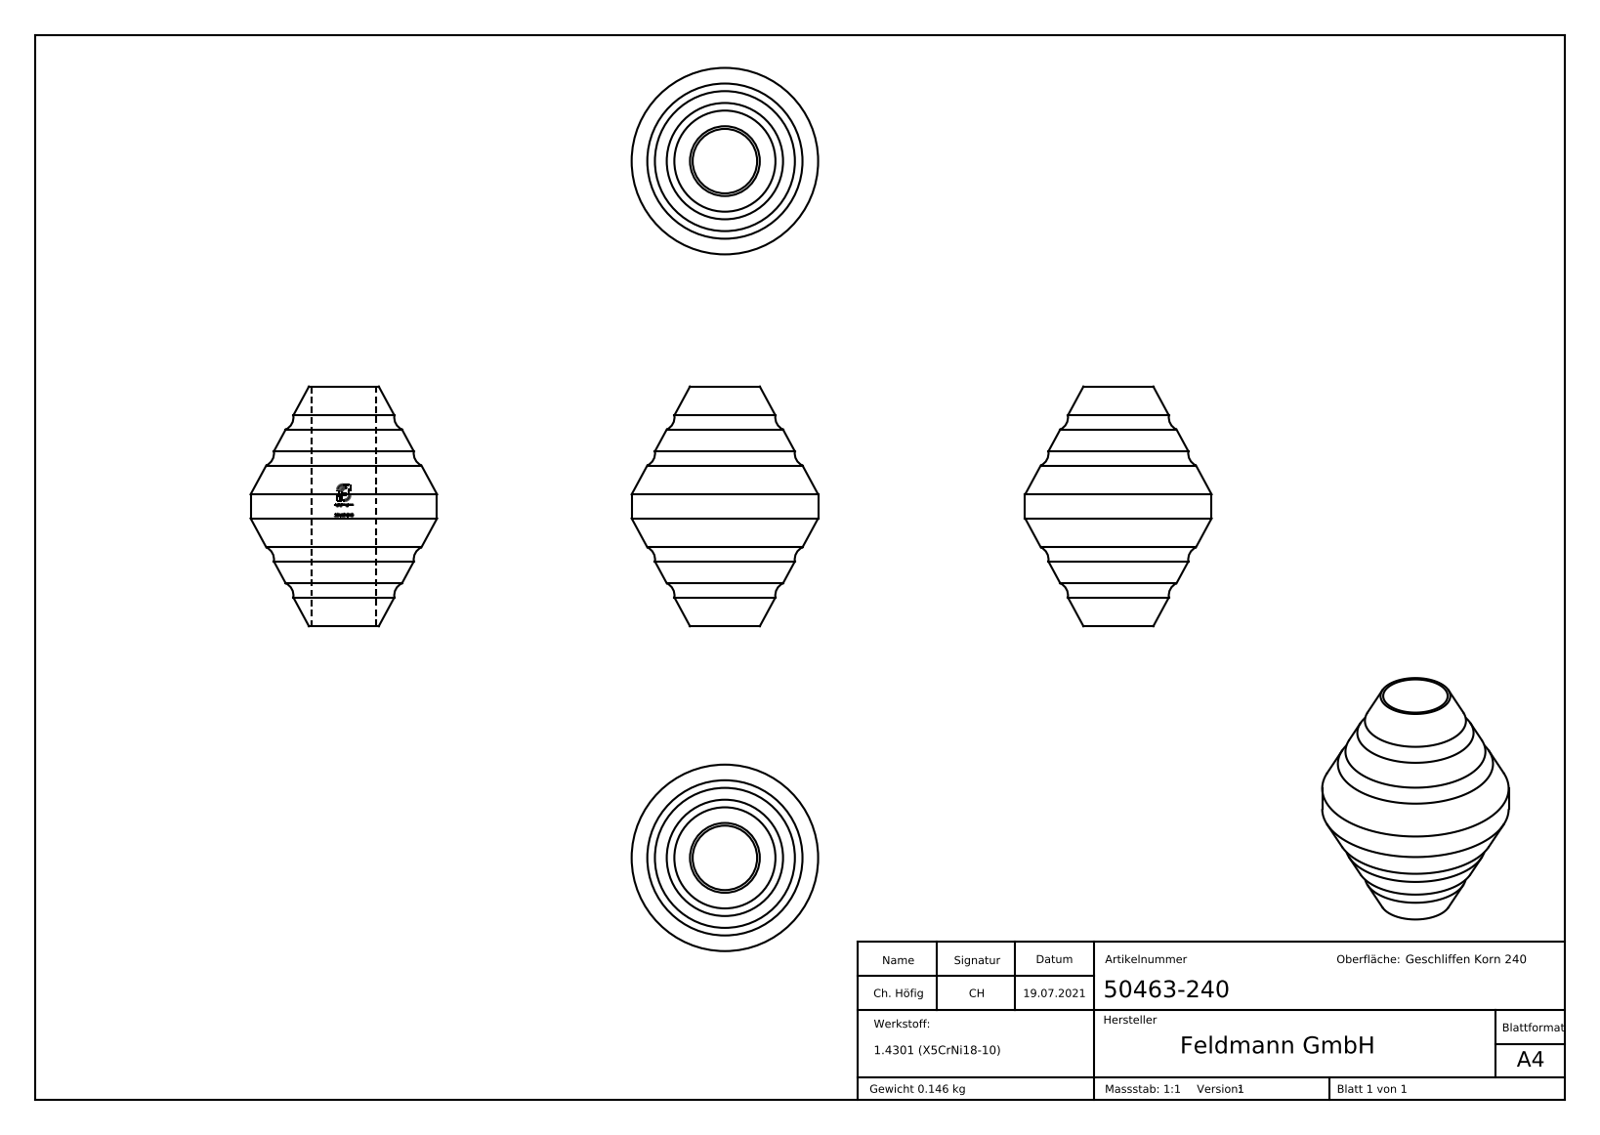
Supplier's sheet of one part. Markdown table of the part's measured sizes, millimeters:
| quantity | value |
| --- | --- |
| part name | 50463-240 |
| STEP written by | SolidWorks 2018 (CONFIG_CONTROL_DESIGN) |
| units | millimeters |
| bodies | 1 solid, 307 faces (126 planar, 30 cylindrical, 151 other) |
| overall size | 45 × 35 × 35 |
| volume | 18 520 mm³ |
| surface area | 5 773 mm² |
| round holes (diameter × count) | 12.1 × 1 |
| round bosses / shafts (diameter × count) | 35 × 1 |
| partial cylindrical surfaces (radius × count) | 6.15 × 1 |
| main face-to-face distances | 45, 0.34, 0.58, 0.32, 1.96, 1.88, 2.45, 1.62, 2.21, 2.2 |
